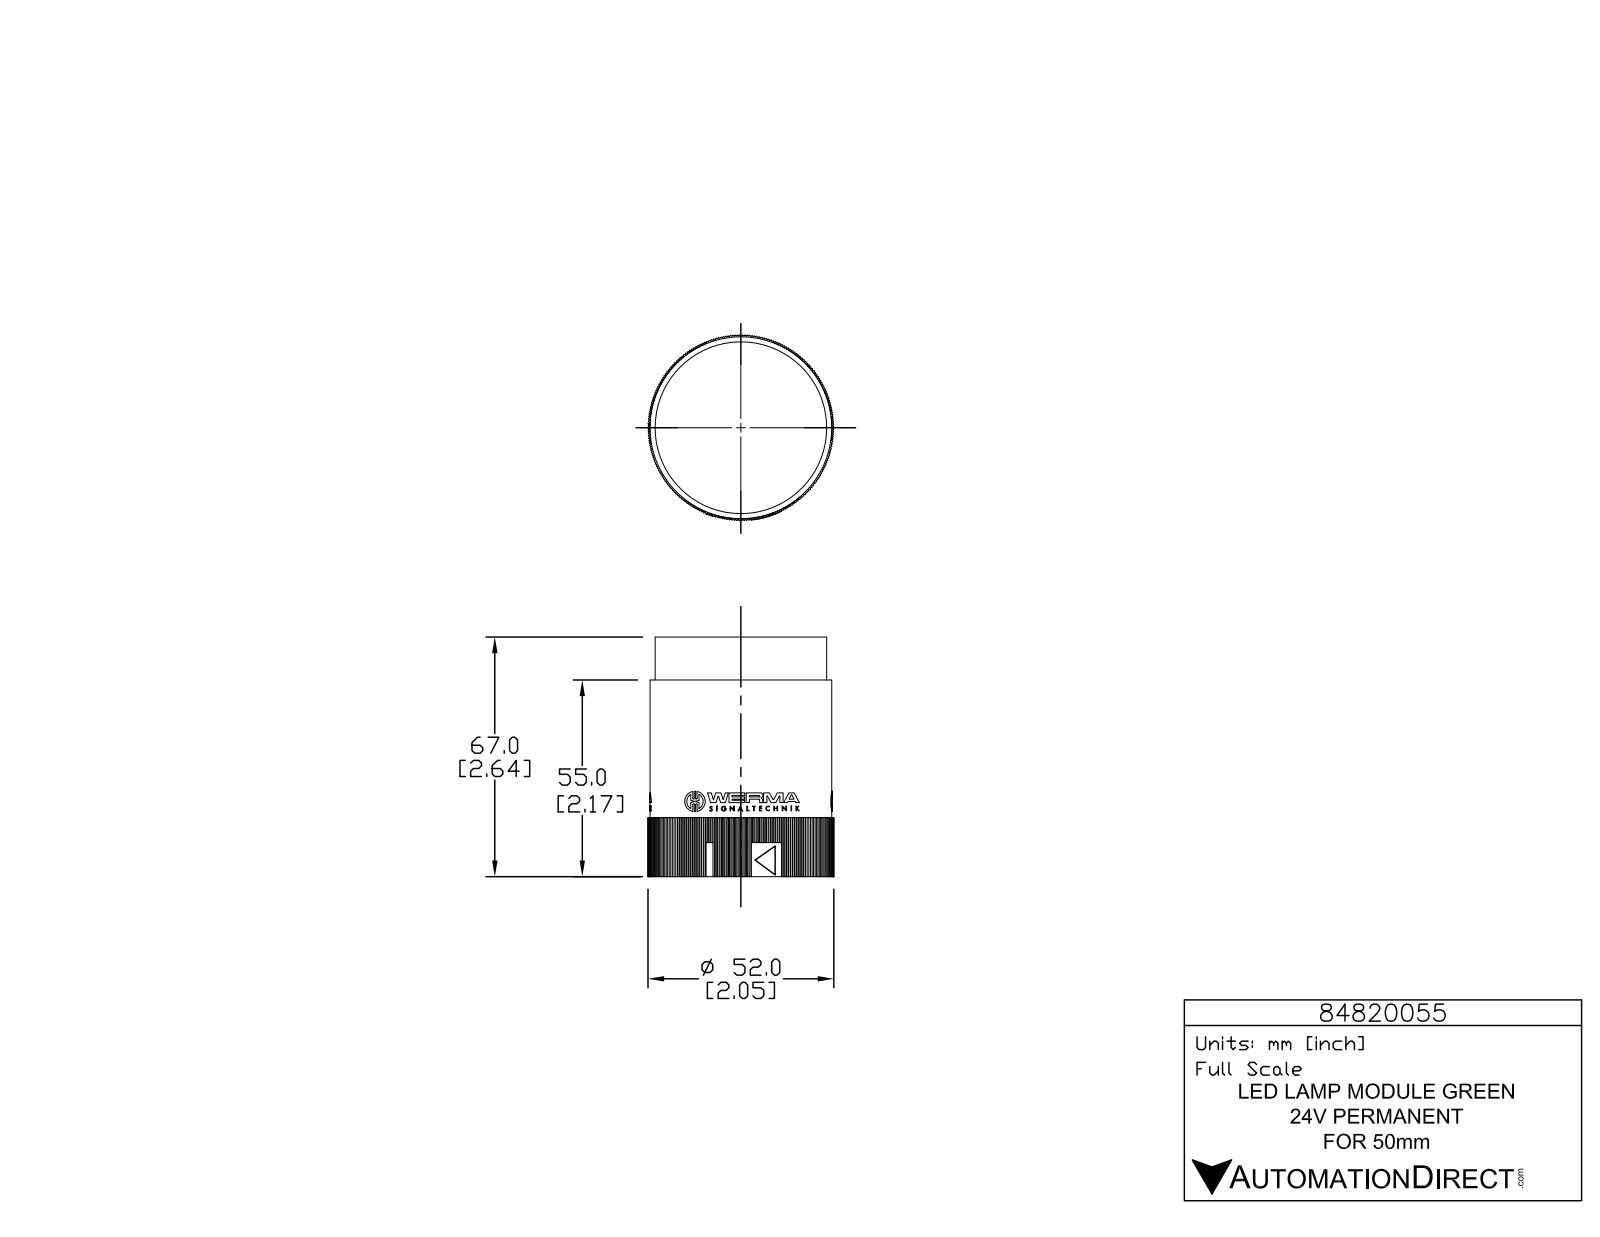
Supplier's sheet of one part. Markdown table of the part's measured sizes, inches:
| quantity | value |
| --- | --- |
| part name | 84820055 |
| STEP written by | SolidWorks 2015 (AUTOMOTIVE_DESIGN) |
| units | inches |
| bodies | 1 solid, 1265 faces (1020 planar, 245 cylindrical, 0 other) |
| overall size | 2.638 × 2.047 × 2.047 |
| volume | 6.873 in³ |
| surface area | 27.62 in² |
| round holes (diameter × count) | 0.039 × 3, 1.898 × 1 |
| round bosses / shafts (diameter × count) | 0.226 × 3, 0.056 × 3, 2.002 × 1, 1.89 × 1 |
| partial cylindrical surfaces (radius × count) | 0.008 × 6, 0.008 × 6, 0.008 × 6, 0.131 × 6, 0.004 × 3, 0.005 × 3, 0.008 × 3, 0.008 × 3 |
| main face-to-face distances | 2.165, 1.428, 1.429, 1.429, 0.472, 2.638, 1.428, 1.428, 1.693, 1.988 |
